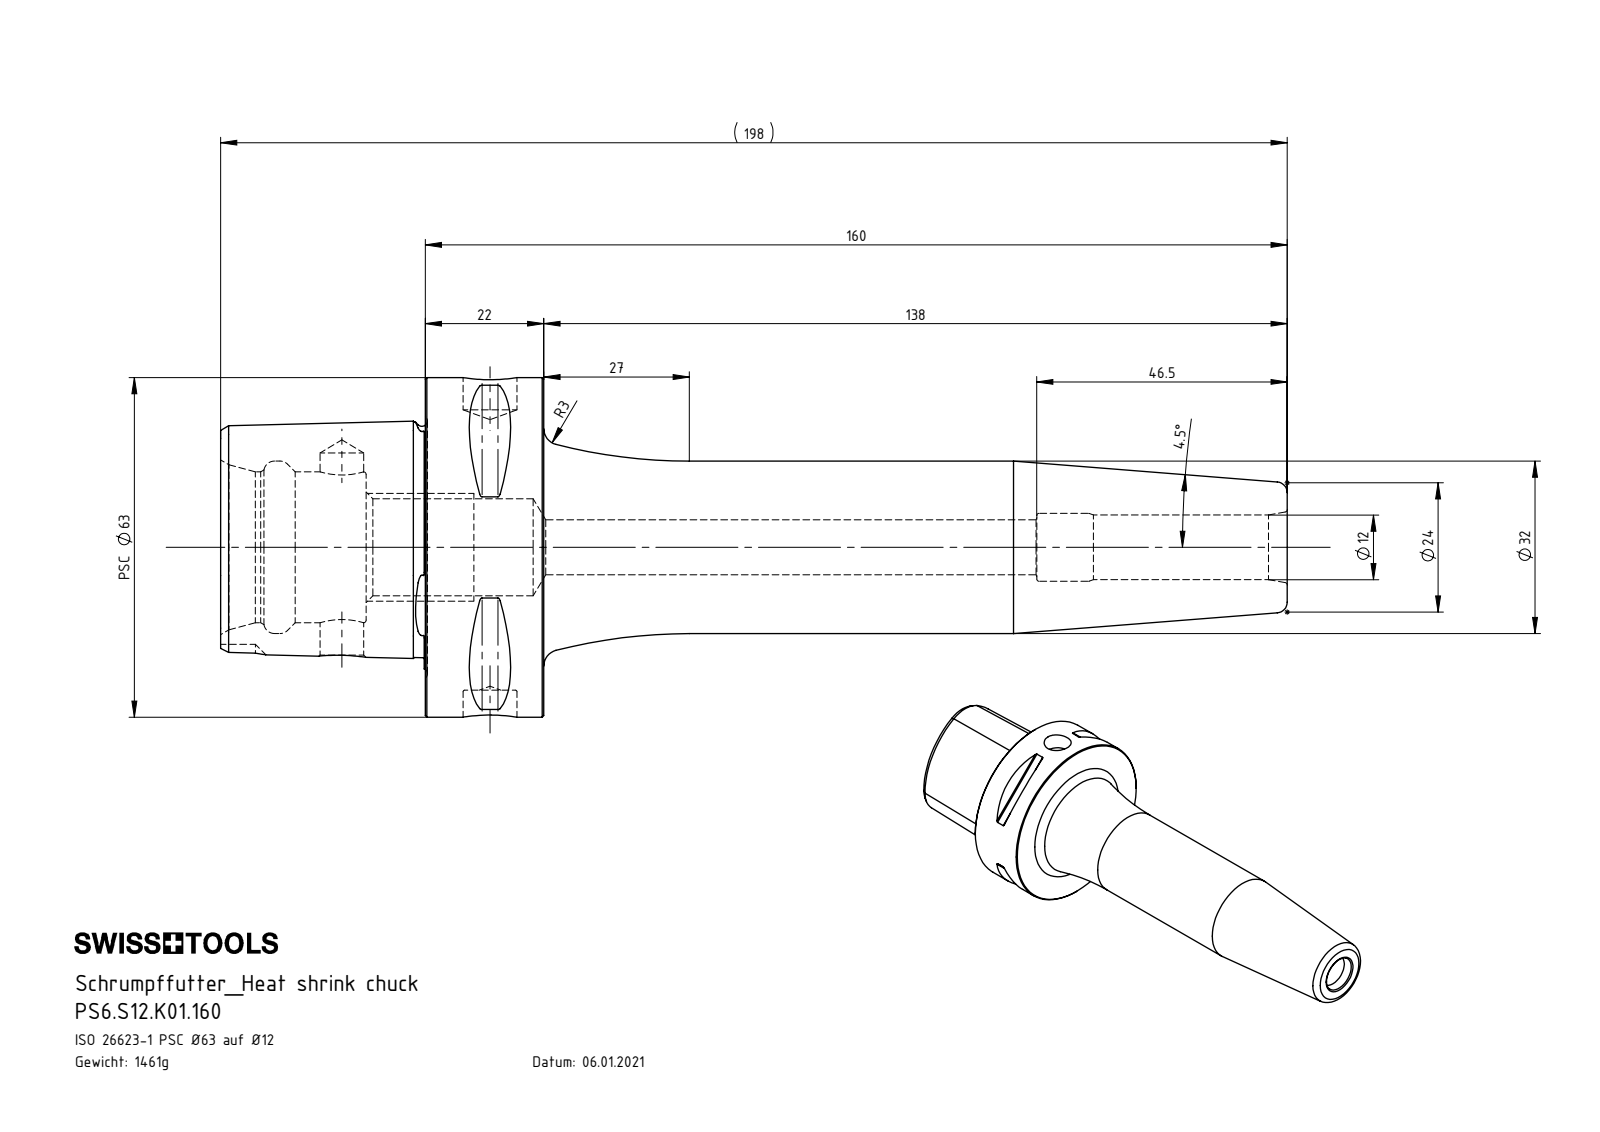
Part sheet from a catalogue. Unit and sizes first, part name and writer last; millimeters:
Units: millimetres
Overall size (bounding box): 198 × 63 × 63
Round holes (diameter × count): ⌀8.1 ×1, ⌀10 ×1, ⌀10.2 ×1, ⌀12 ×1, ⌀12.6 ×1, ⌀18 ×1, ⌀28 ×1, ⌀32 ×1
Round bosses / shafts (diameter × count): ⌀63 ×1
Partial cylindrical surfaces — rounded edges, fillets, slot ends (radius × count): R0.5 ×8, R6 ×1
Main face-to-face distances: 22, 38, 60, 24.88, 27, 11, 33, 55.8, 198, 171
Hole centre spacings: 27.5
Volume: 186 156 mm³ · Surface area: 37 619 mm²
Bodies: 1 solid, 154 faces (22 planar, 35 cylindrical, 97 other)
Part name (STEP PRODUCT): PS6.S12.K01.160
STEP written by: SolidWorks 2022 (AUTOMOTIVE_DESIGN)
